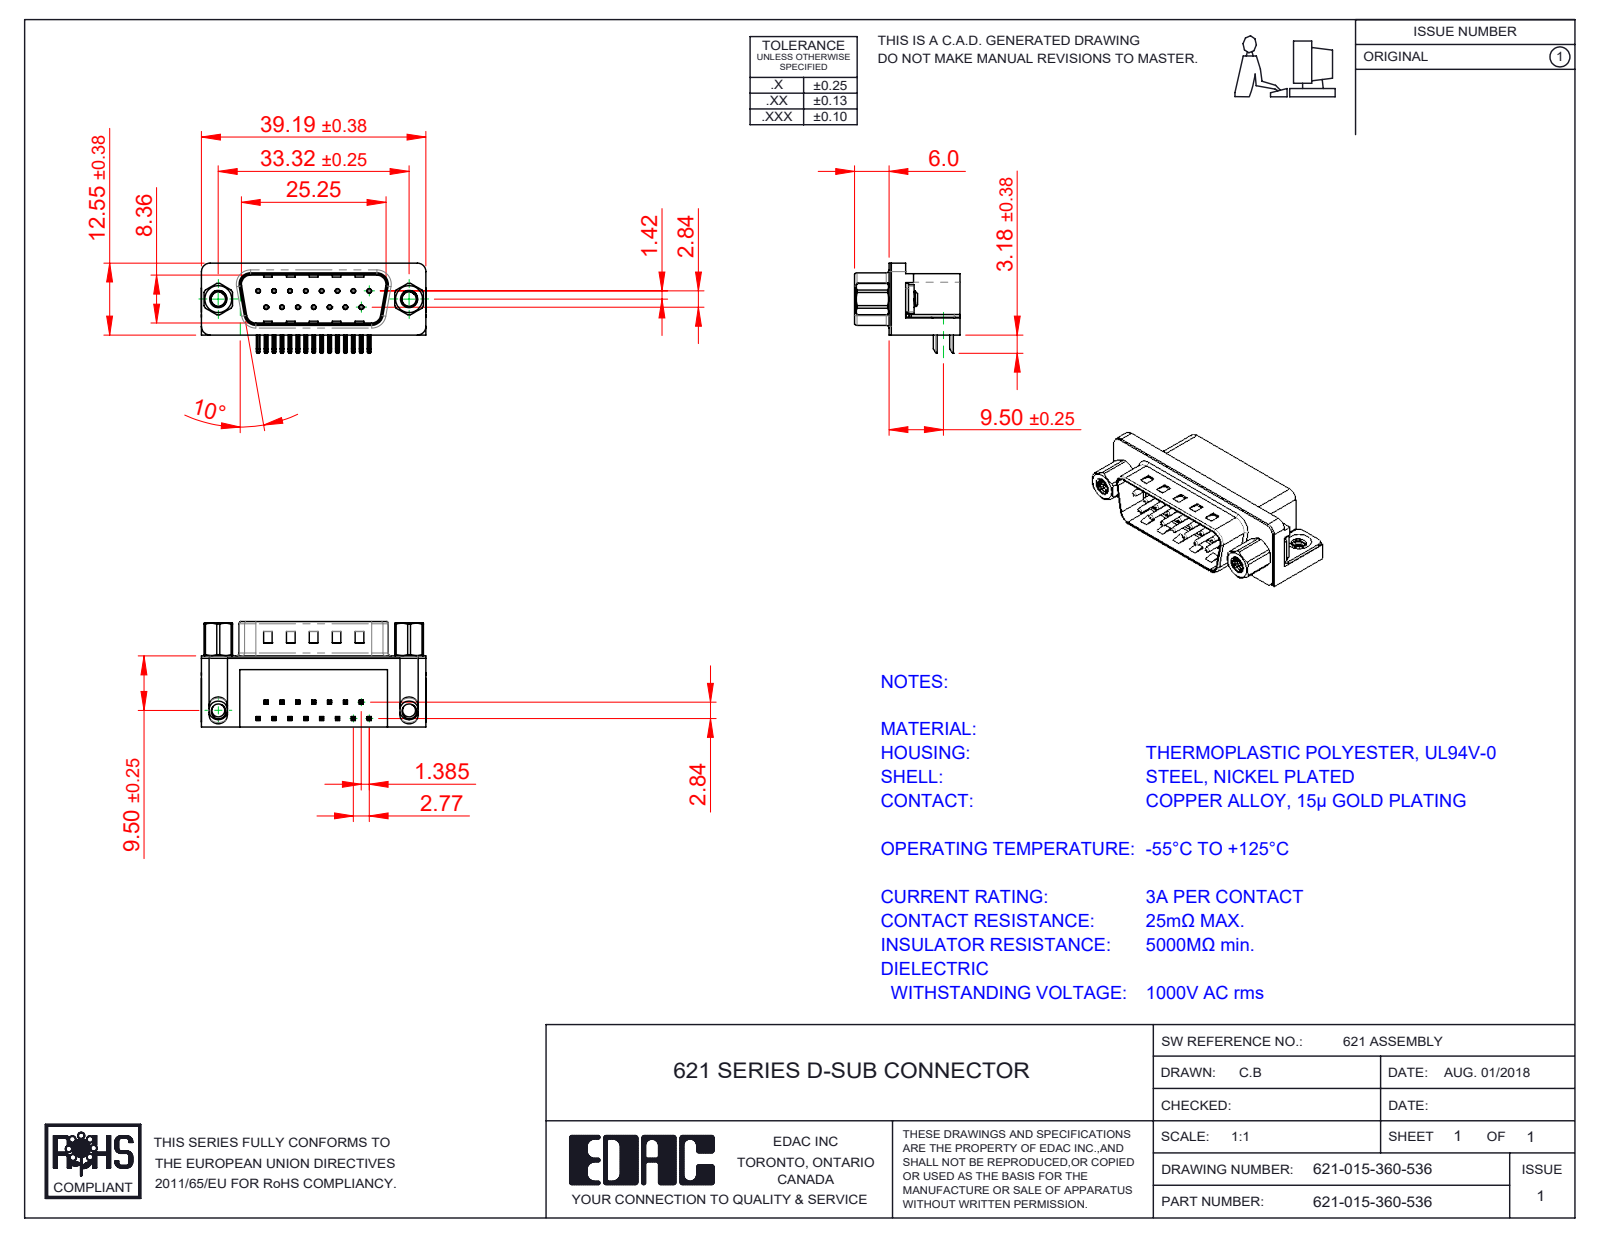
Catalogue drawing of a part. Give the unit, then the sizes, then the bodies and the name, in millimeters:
Units: millimetres
Overall size (bounding box): 39.22 × 18.4 × 16.25
Round holes (diameter × count): ⌀0.35 ×15, ⌀0.8 ×15, ⌀2.5 ×2, ⌀4 ×2, ⌀4.8 ×2, ⌀5 ×2
Round bosses / shafts (diameter × count): ⌀0.75 ×15, ⌀4.9 ×2, ⌀4.75 ×2, ⌀3.9 ×2, ⌀3 ×2
Partial cylindrical surfaces — rounded edges, fillets, slot ends (radius × count): R0.25 ×68, R0.12 ×30, R1 ×16, R0.5 ×14, R1.6 ×8, R1.5 ×6, R0.32 ×4, R0.9 ×4
Main face-to-face distances: 0.4, 12, 10.35, 12.4, 2.1, 10.46, 1.7, 10.86, 8.76, 9.5
Hole centre spacings: 3.16, 2.77, 5.54, 8.31, 11.08, 5.03, 5.04, 7.48
Volume: 4 654 mm³ · Surface area: 6 188 mm²
Bodies: 23 solids, 1665 faces (947 planar, 549 cylindrical, 169 other)
Part name (STEP PRODUCT): 621 M3 Hex Standoff 5; 621 M3 Threaded Rivet; 621 2 Prong Board Lock; 621-015-360-536 (+4 more)
STEP written by: SolidWorks 2016 (CONFIG_CONTROL_DESIGN)
